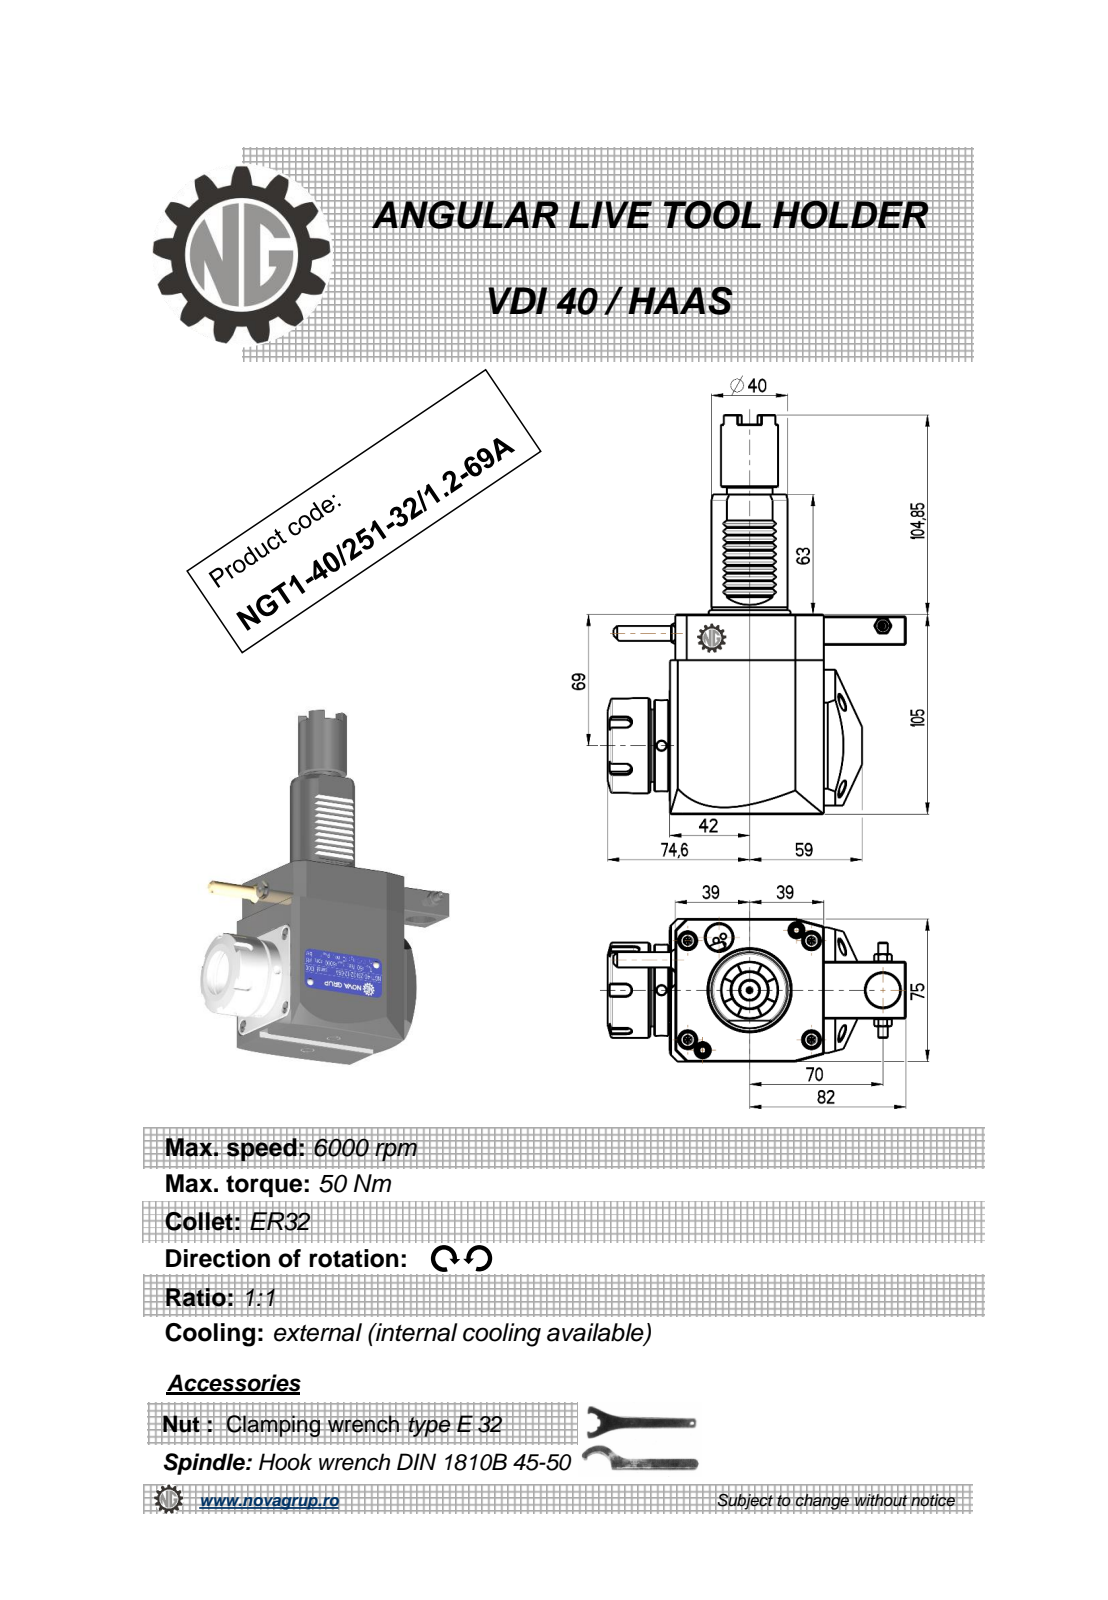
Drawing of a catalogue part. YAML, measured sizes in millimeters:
part_name: "NGT1_40_251_32_1_2_69A"
step_written_by: "PRO/ENGINEER BY PARAMETRIC TECHNOLOGY CORPORATION, 2010280 (CONFIG_CONTROL_DESIGN)"
units: millimeters
bodies: {solids: 1, faces: 453, planar: 222, cylindrical: 94, other: 137}
overall_size: [209.85, 156.6, 76.6]
volume: 846838
surface_area: 72623
round_holes:
  - {diameter: 5, count: 3}
  - {diameter: 3, count: 1}
  - {diameter: 4.2, count: 1}
  - {diameter: 9.5, count: 1}
  - {diameter: 18, count: 1}
  - {diameter: 27, count: 1}
round_bosses_or_shafts:
  - {diameter: 50, count: 1}
  - {diameter: 48, count: 1}
  - {diameter: 41, count: 1}
  - {diameter: 40, count: 1}
  - {diameter: 30, count: 1}
  - {diameter: 24, count: 1}
  - {diameter: 10, count: 1}
  - {diameter: 8.96, count: 1}
partial_cylinders:
  - {radius: 0.26, count: 12}
  - {radius: 0.3, count: 10}
  - {radius: 0.2, count: 6}
  - {radius: 3, count: 5}
  - {radius: 0.5, count: 1}
  - {radius: 9.75, count: 1}
  - {radius: 40, count: 1}
face_to_face_distances: [75, 105, 81, 80.8, 1, 22.5, 3, 89, 2.8, 78]
hole_center_spacings: [16.19, 61.13, 61.5, 116.25, 132.22]
